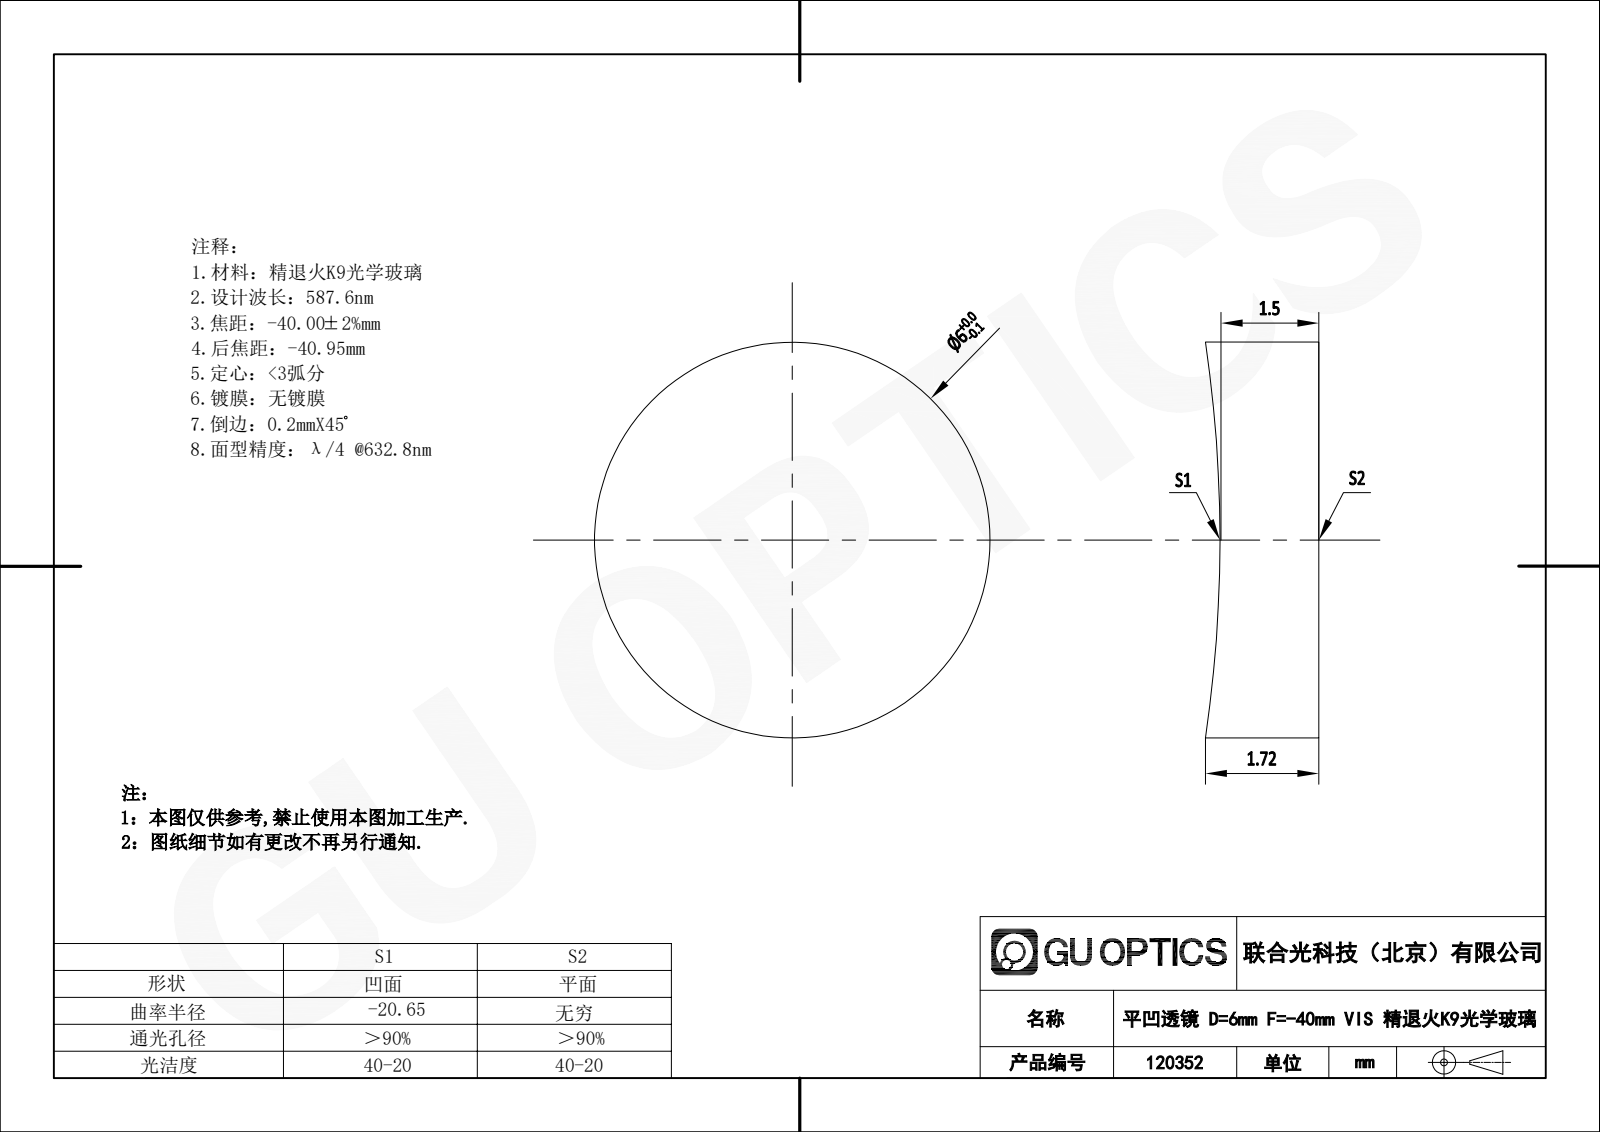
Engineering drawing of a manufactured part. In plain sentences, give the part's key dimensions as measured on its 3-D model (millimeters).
The part is named "120352". Its 3-D file was written by "SolidWorks 2020 (CONFIG_CONTROL_DESIGN)". It is 1 solid with 5 faces: 1 planar, 2 cylindrical and 2 other. Overall it measures 6 by 6 by 1.72 millimeters. Its volume is 46 cubic millimeters and its surface area 89 square millimeters. Round bosses or shafts: 1 of diameter 6.
